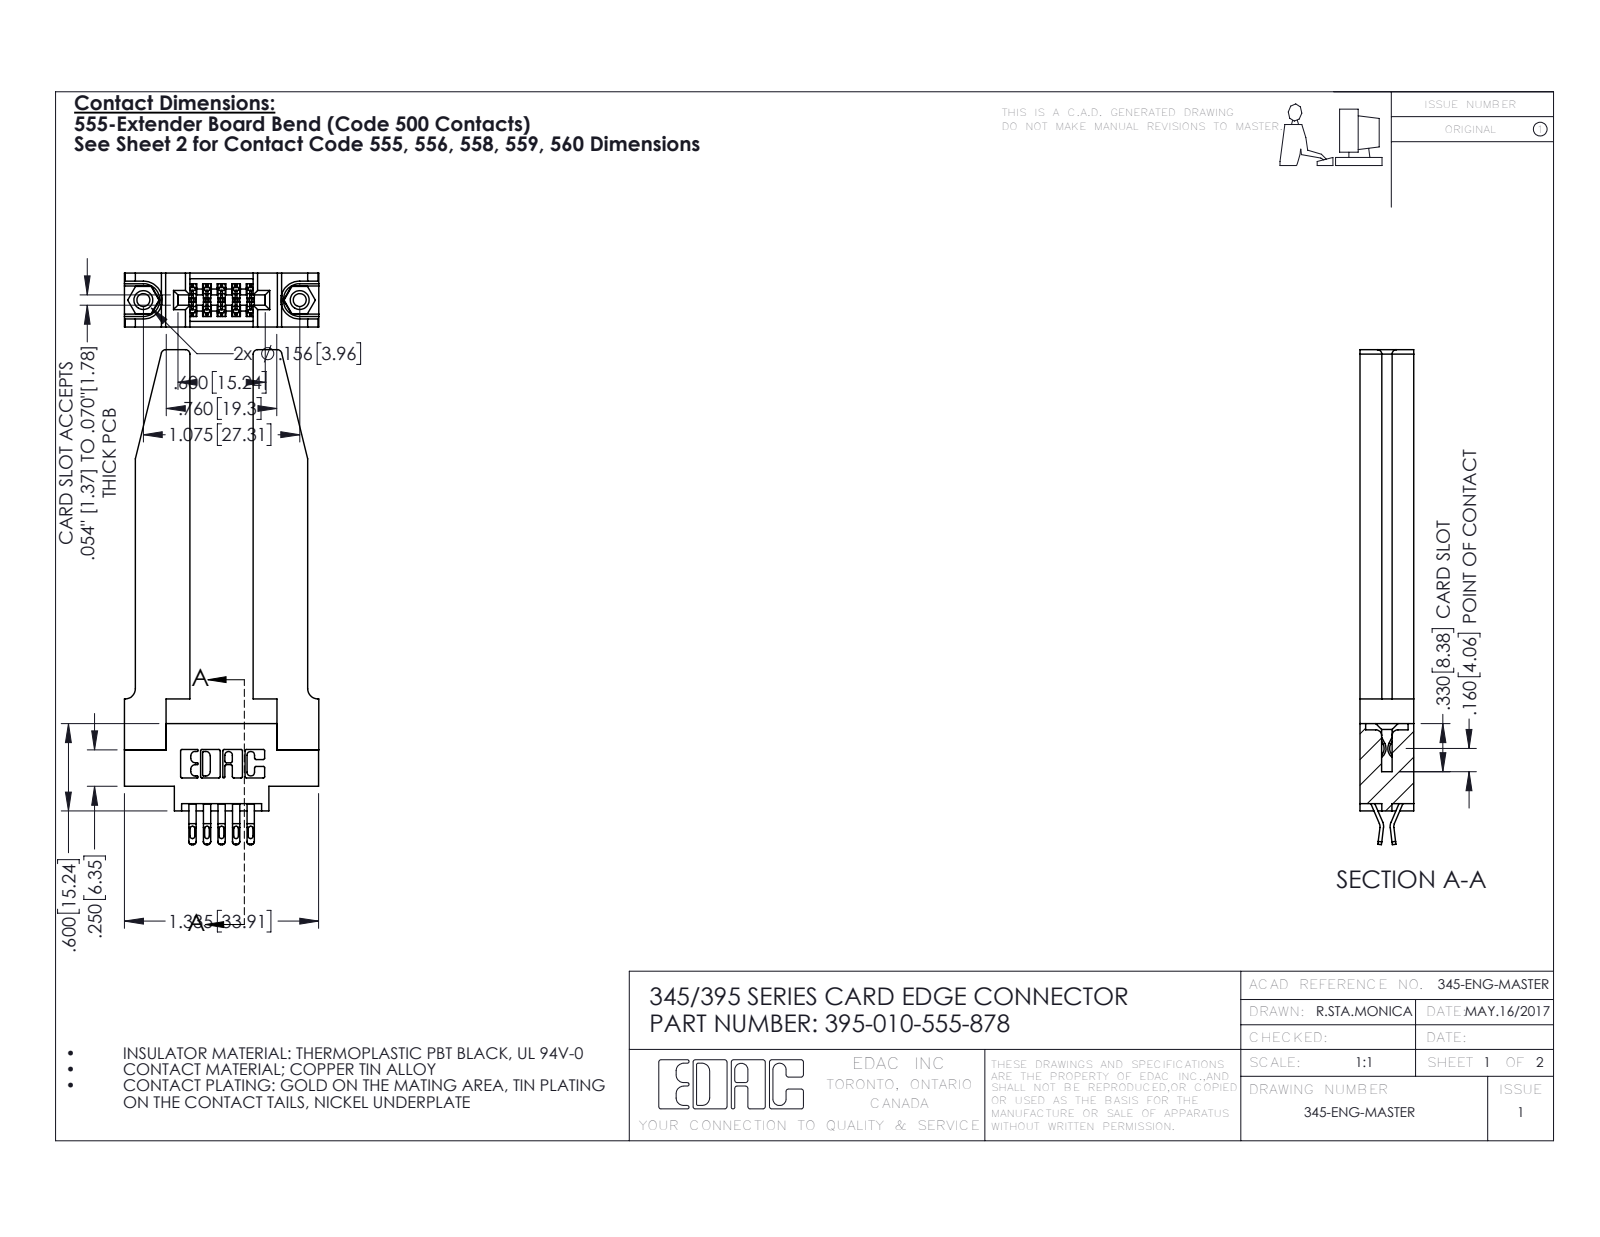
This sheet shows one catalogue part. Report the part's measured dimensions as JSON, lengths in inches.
{"part_name": "345 Part_0.170 Offset - 0.156 Dia-TH; 395-010-555-878; 345-220-078_345-220-078; 345-250-001_345-250-001-102 (+1 more)", "step_written_by": "SolidWorks 2016 (CONFIG_CONTROL_DESIGN)", "units": "inches", "bodies": {"solids": 15, "faces": 924, "planar": 536, "cylindrical": 336, "other": 52}, "overall_size": [3.402, 1.336, 0.37], "volume_in3": 0.649, "surface_area_in2": 16.44, "round_holes": [[0.089, 2], [0.125, 2], [0.156, 2], [0.064, 1]], "round_bosses_or_shafts": [[0.155, 2]], "partial_cylinders_radius": [[0.016, 25], [0.01, 22], [0.02, 20], [0.006, 15], [0.03, 8], [0.007, 6], [0.031, 6], [0.026, 3]], "face_to_face_distances": [0.37, 0.15, 0.22, 0.435, 0.072, 0.148, 0.298, 0.077, 0.095, 0.071], "hole_center_spacings": [0.27, 0.847, 1.075]}
